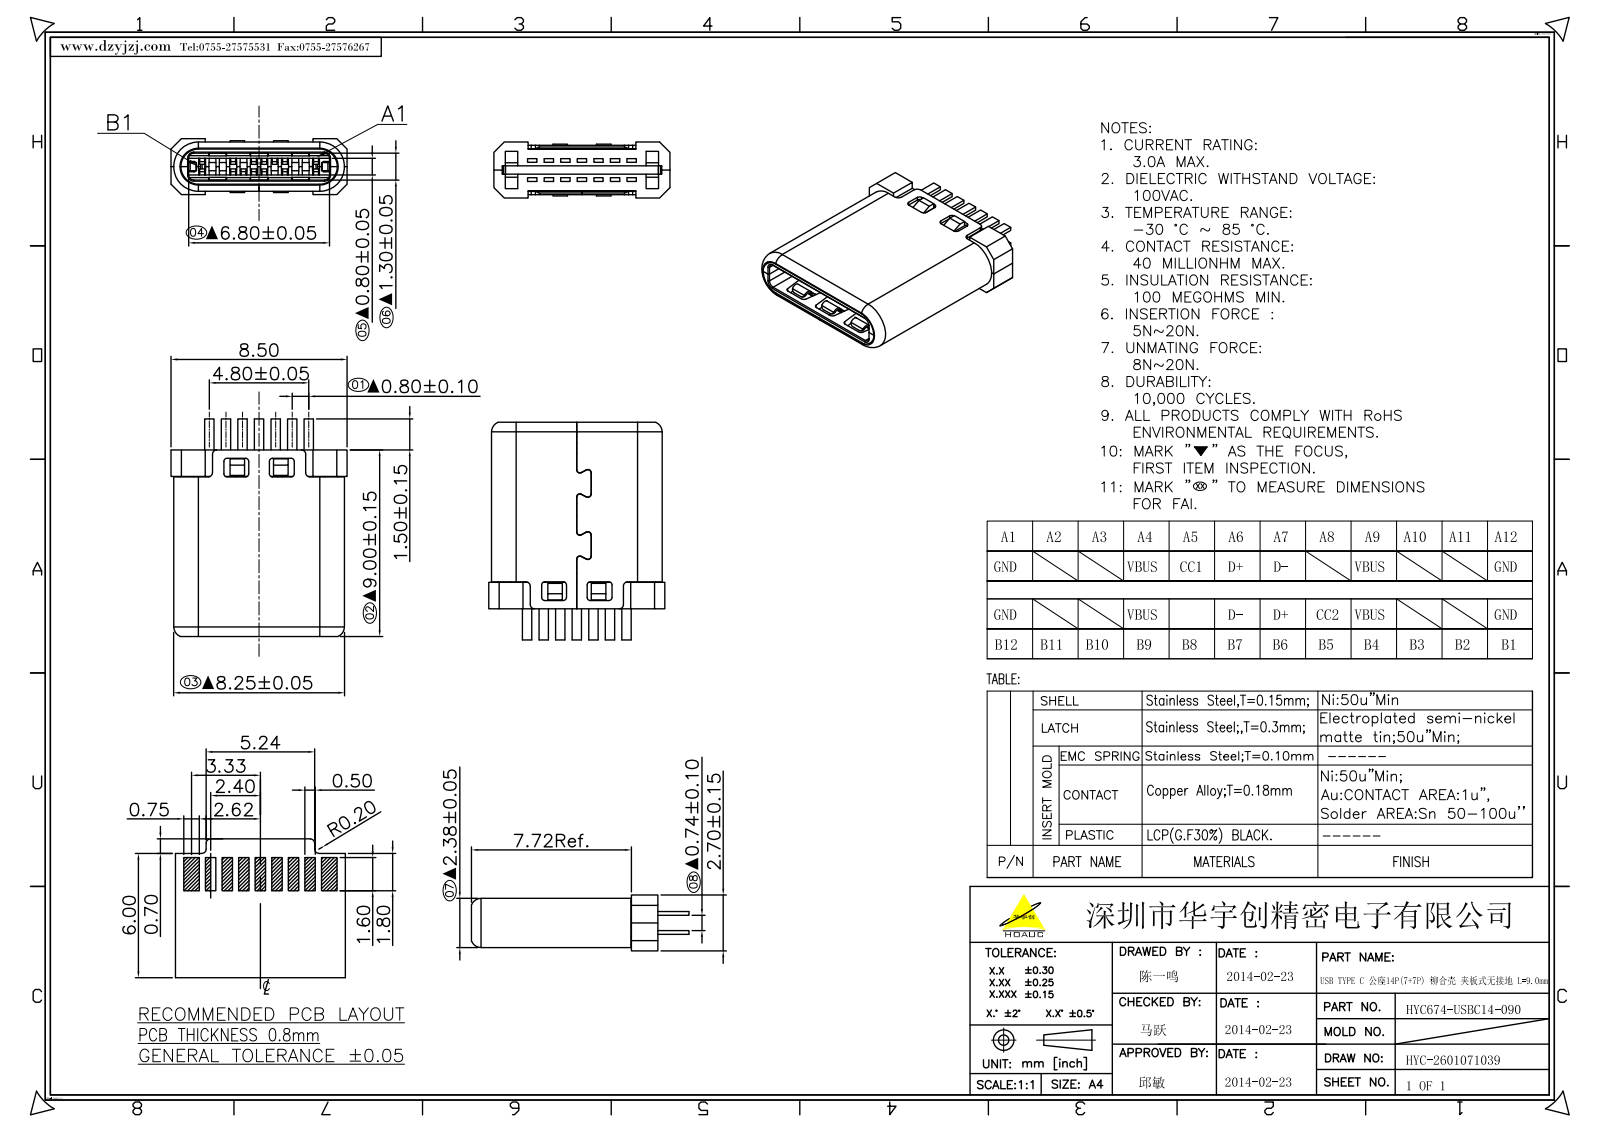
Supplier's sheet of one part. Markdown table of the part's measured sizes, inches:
| quantity | value |
| --- | --- |
| part name | STD-TYPE_C_7P_L_9_0MM_ASM |
| STEP written by | CREO PARAMETRIC BY PTC INC, 2022073 (AUTOMOTIVE_DESIGN) |
| units | inches |
| bodies | 1 solid, 562 faces (410 planar, 123 cylindrical, 29 other) |
| overall size | 0.413 × 0.335 × 0.106 |
| volume | 0.008 in³ |
| surface area | 0.584 in² |
| round holes (diameter × count) | 0.039 × 2 |
| partial cylindrical surfaces (radius × count) | 0.006 × 16, 0.008 × 8, 0.01 × 6, 0.004 × 4, 0.005 × 4, 0.006 × 4, 0.006 × 4, 0.006 × 3 |
| main face-to-face distances | 0.094, 0.031, 0.063, 0.031, 0.041, 0.021, 0.072, 0.037, 0.03, 0.047 |
| hole center spacings | 0.157 |
